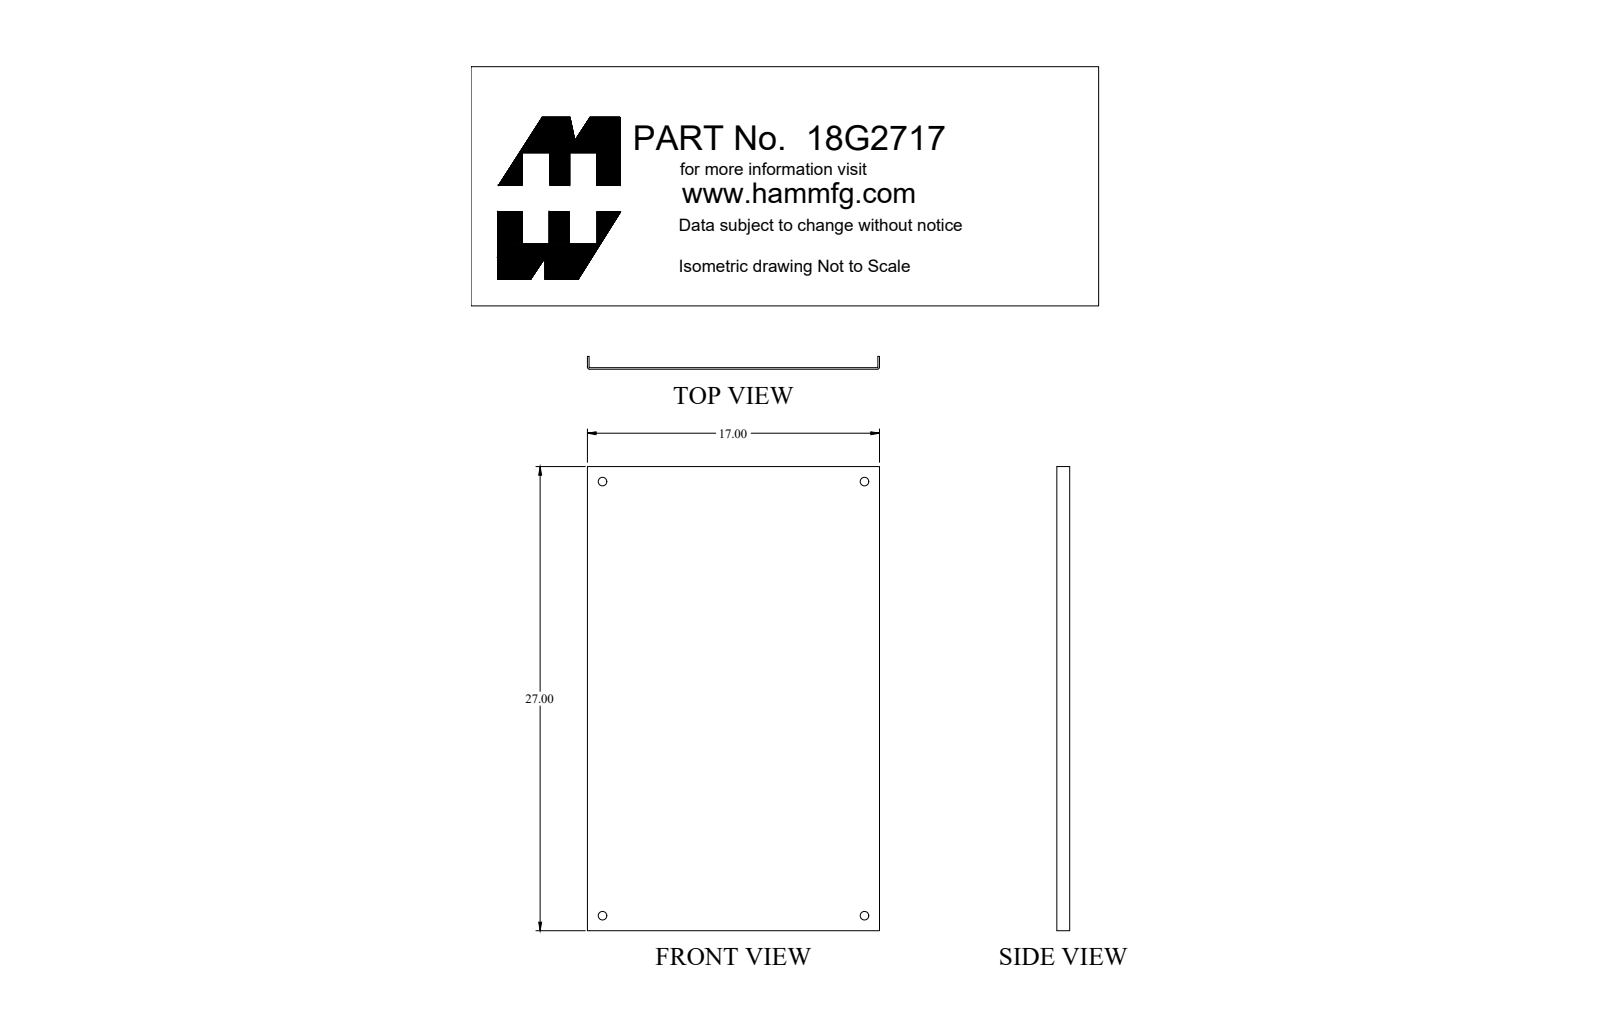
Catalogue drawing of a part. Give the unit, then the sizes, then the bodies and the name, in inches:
Units: inches
Overall size (bounding box): 27 × 17 × 0.75
Round holes (diameter × count): ⌀0.5 ×4
Partial cylindrical surfaces — rounded edges, fillets, slot ends (radius × count): R0.03 ×2, R0.125 ×2
Main face-to-face distances: 0.095, 16.905, 17, 16.81, 0.75, 0.655, 27
Hole centre spacings: 15.25, 25.25, 29.497
Volume: 46.72 in³ · Surface area: 992.8 in²
Bodies: 1 solid, 18 faces (10 planar, 8 cylindrical, 0 other)
Part name (STEP PRODUCT): 18G2717
STEP written by: SolidWorks 2018 (AUTOMOTIVE_DESIGN)
